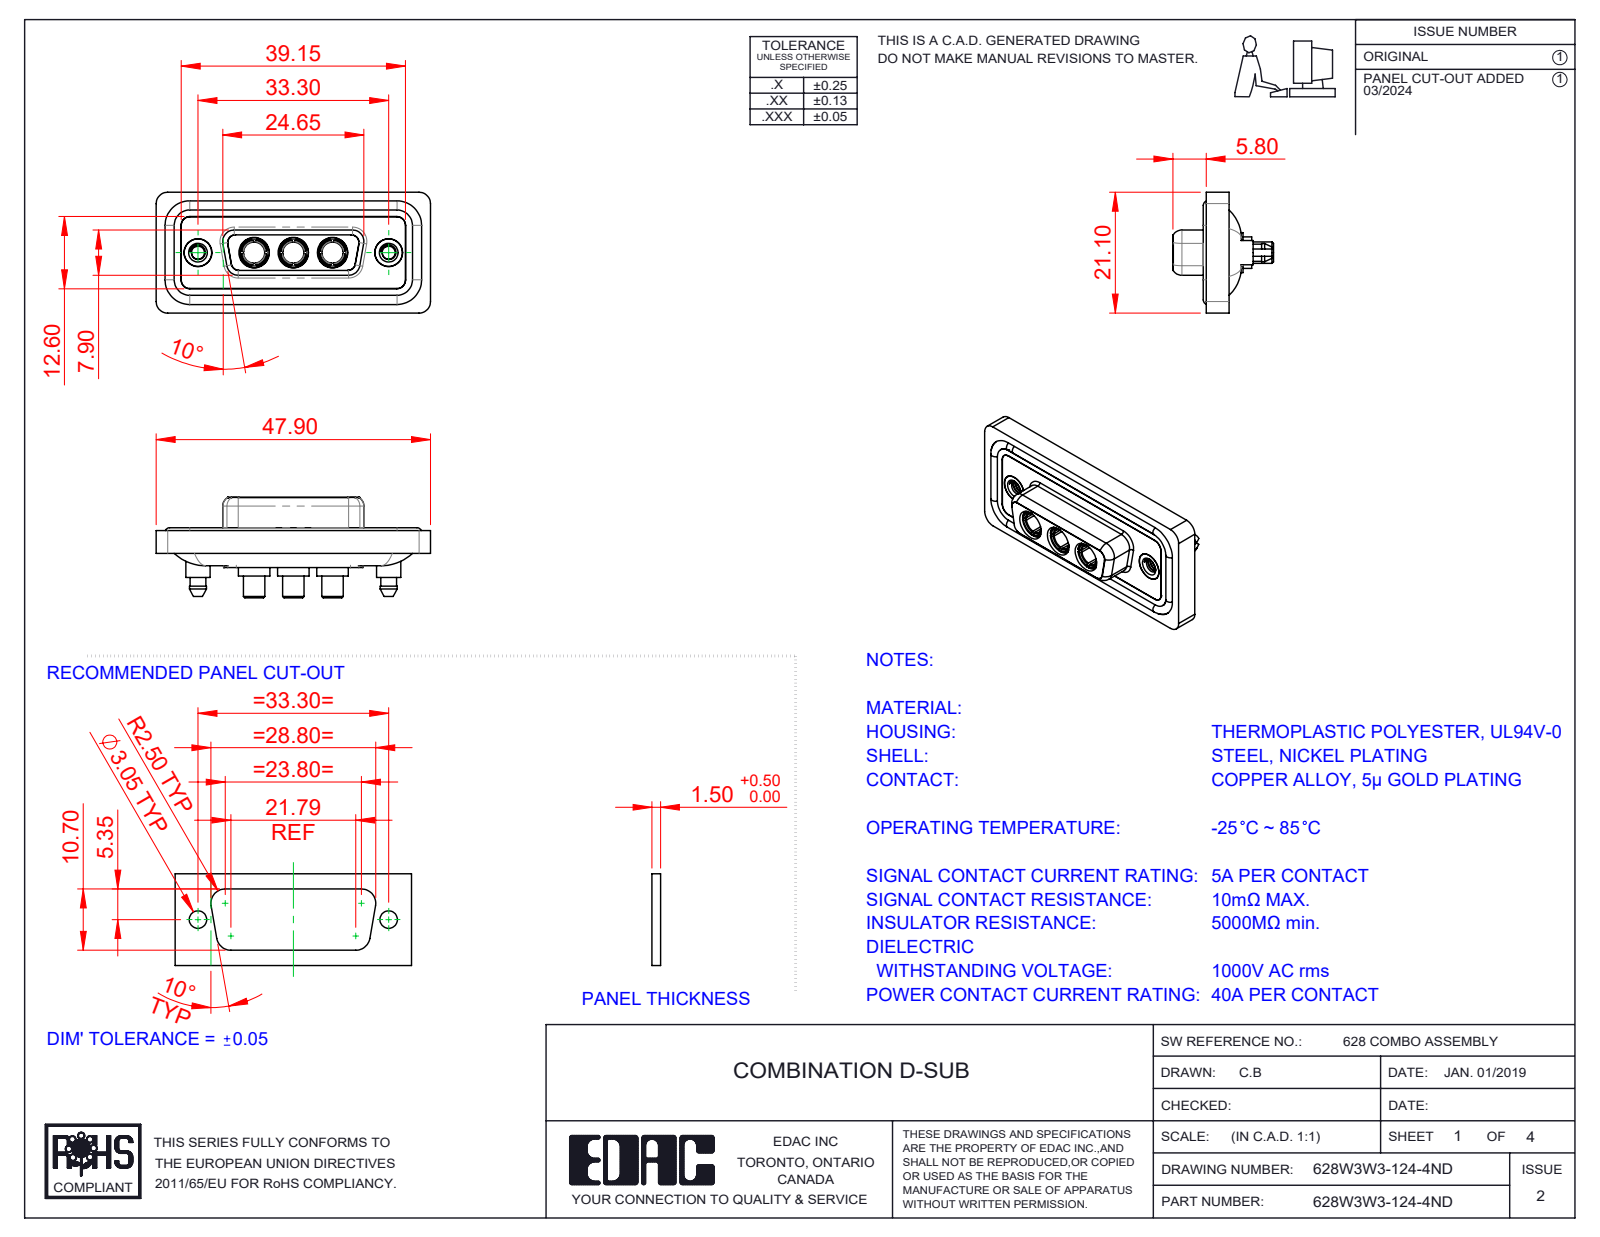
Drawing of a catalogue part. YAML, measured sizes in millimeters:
part_name: "Power Socket_40A S; 628Combo Threaded Boardlock_D; 628W3W3-124-4ND; 628Combo Shell Rear_15 Contacts (+3 more)"
step_written_by: "SolidWorks 2023 (CONFIG_CONTROL_DESIGN)"
units: millimeters
bodies: {solids: 13, faces: 674, planar: 208, cylindrical: 305, other: 161}
overall_size: [47.9, 21.1, 17.55]
volume: 6217
surface_area: 10110
round_holes:
  - {diameter: 4.85, count: 5}
  - {diameter: 3.7, count: 3}
  - {diameter: 5.3, count: 3}
  - {diameter: 2.26, count: 2}
  - {diameter: 4, count: 2}
  - {diameter: 4.05, count: 2}
  - {diameter: 5, count: 2}
round_bosses_or_shafts:
  - {diameter: 1.6, count: 4}
  - {diameter: 5.5, count: 3}
  - {diameter: 5.2, count: 3}
  - {diameter: 4.96, count: 3}
  - {diameter: 4.75, count: 3}
  - {diameter: 3.75, count: 3}
  - {diameter: 5.4, count: 2}
  - {diameter: 4.95, count: 2}
partial_cylinders:
  - {radius: 1.5, count: 24}
  - {radius: 2, count: 20}
  - {radius: 1.35, count: 12}
  - {radius: 1.6, count: 10}
  - {radius: 0.25, count: 4}
  - {radius: 0.5, count: 4}
  - {radius: 0.6, count: 4}
  - {radius: 0.65, count: 4}
face_to_face_distances: [0.4, 1.8, 1.6, 0.5, 7.45, 1.1, 2.9, 5.65, 7.05, 6.6]
hole_center_spacings: [6.85, 9.8, 16.65, 23.5, 13.7, 33.3]
